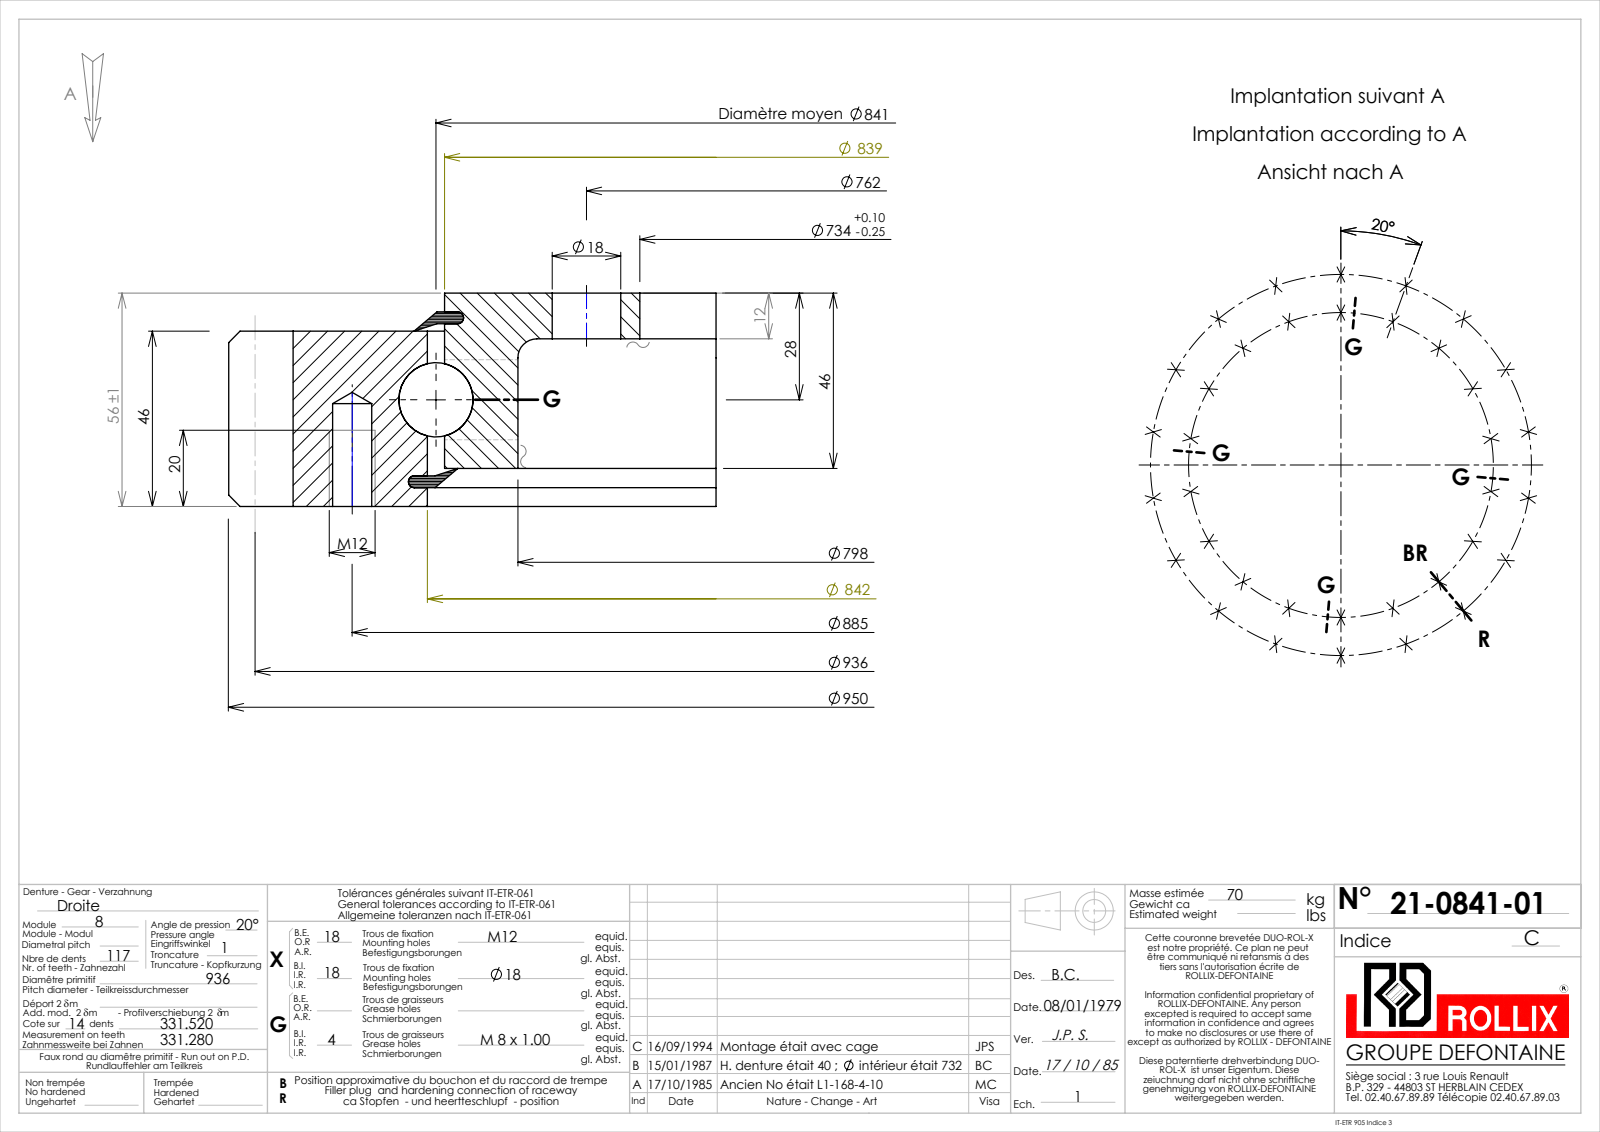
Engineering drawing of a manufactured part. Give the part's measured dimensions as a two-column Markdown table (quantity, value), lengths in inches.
| quantity | value |
| --- | --- |
| part name | 21-0841-01 |
| STEP written by | SolidWorks 2016 (CONFIG_CONTROL_DESIGN) |
| units | inches |
| bodies | 9 solids, 967 faces (287 planar, 339 cylindrical, 341 other) |
| overall size | 37.401 × 37.398 × 2.205 |
| volume | 510.2 in³ |
| surface area | 2 133 in² |
| round holes (diameter × count) | 0.404 × 18, 0.709 × 18, 0.276 × 4, 28.898 × 1, 31.417 × 1, 33.287 × 1 |
| round bosses / shafts (diameter × count) | 0.315 × 4, 32.933 × 1 |
| partial cylindrical surfaces (radius × count) | 18.031 × 1, 18.701 × 1 |
| main face-to-face distances | 0.394, 1.811, 2.205, 1.732, 0.079, 0.472, 1.339, 1.417, 0.317, 1.888 |
| hole center spacings | 17.421, 11.32, 15, 16.346, 30.477, 6.05, 11.917, 20.922 |
